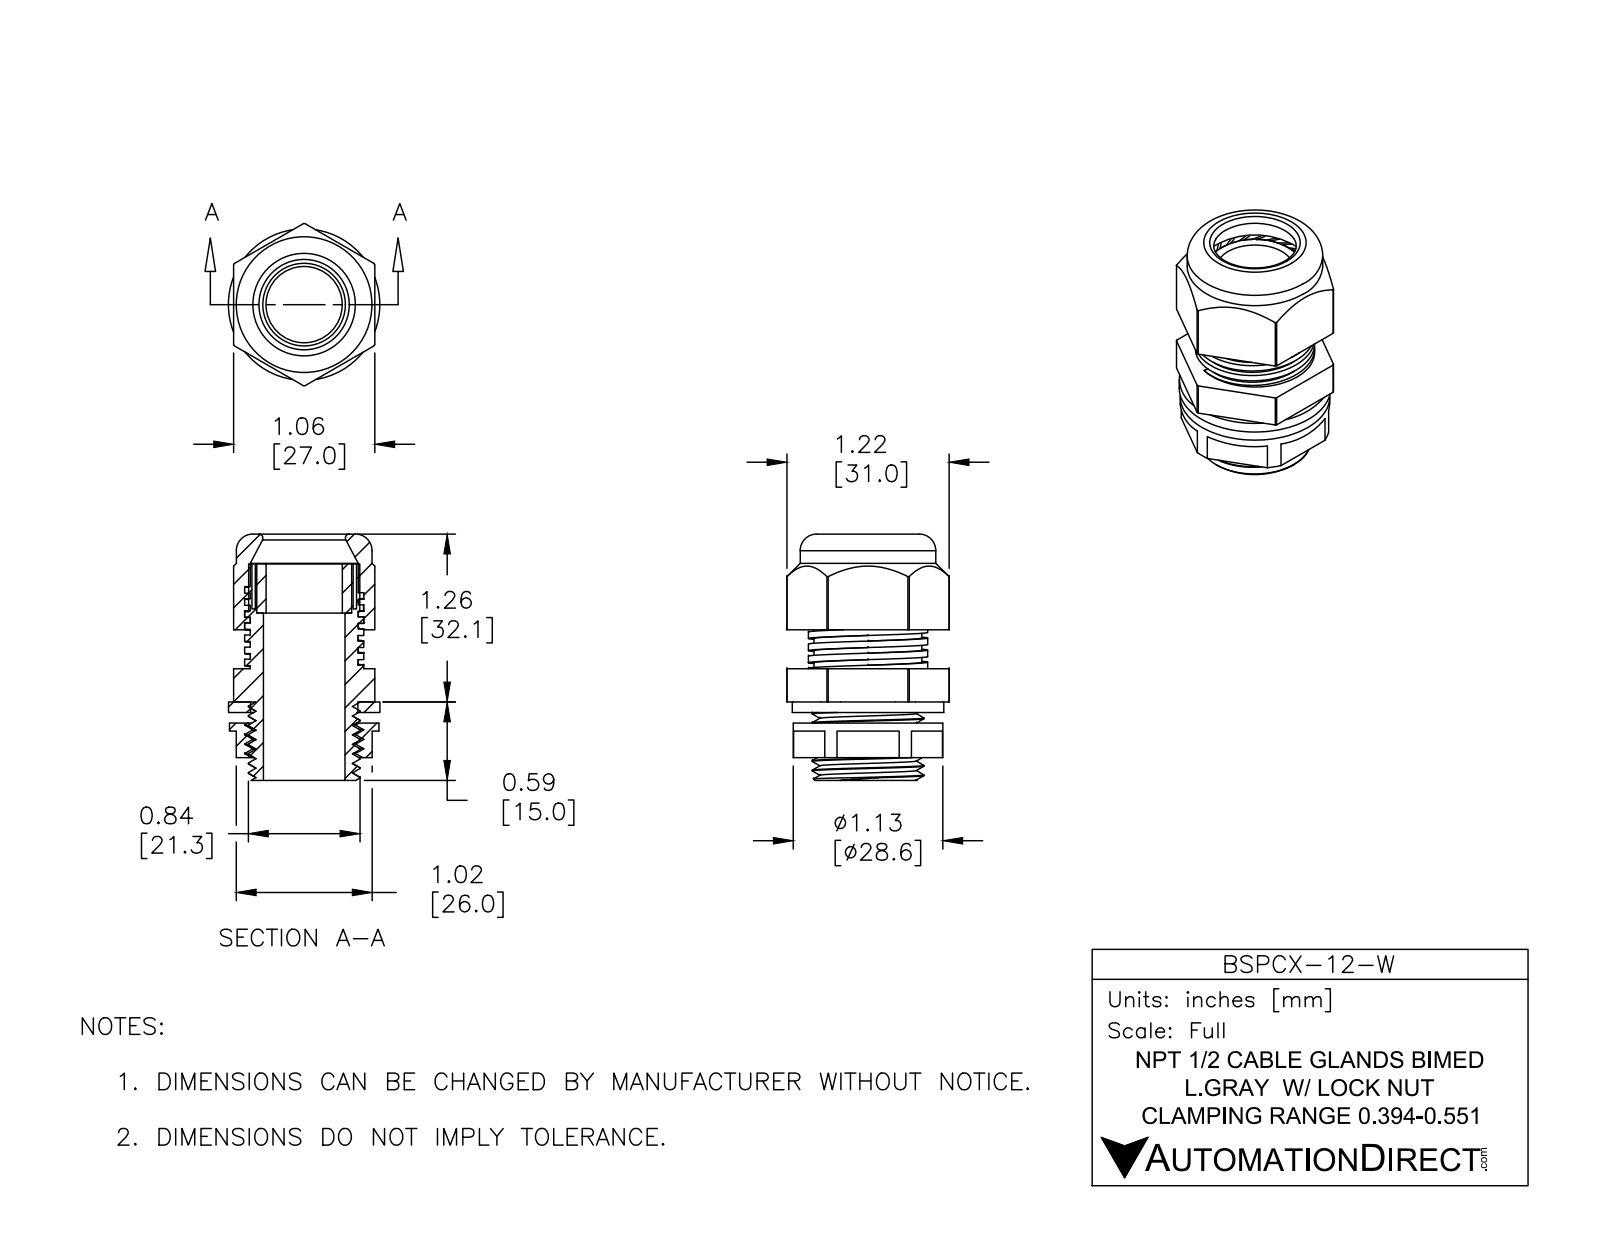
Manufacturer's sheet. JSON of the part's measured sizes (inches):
{"part_name": "BSPCX-12-W", "step_written_by": "SolidWorks 2015 (CONFIG_CONTROL_DESIGN)", "units": "inches", "bodies": {"solids": 5, "faces": 230, "planar": 128, "cylindrical": 76, "other": 26}, "overall_size": [1.853, 1.22, 1.14], "volume_in3": 0.919, "surface_area_in2": 24.81, "round_holes": [[0.573, 1], [0.613, 1], [0.715, 1], [0.783, 1], [0.808, 1], [0.813, 1]], "round_bosses_or_shafts": [[1.14, 1], [1.125, 1], [1.02, 1], [0.897, 1], [0.84, 1], [0.836, 1]], "partial_cylinders_radius": [[0.61, 1]], "face_to_face_distances": [1.062, 0.02, 0.419, 0.669, 1.043, 0.079, 0.08, 0.159, 0.02, 0.409]}
